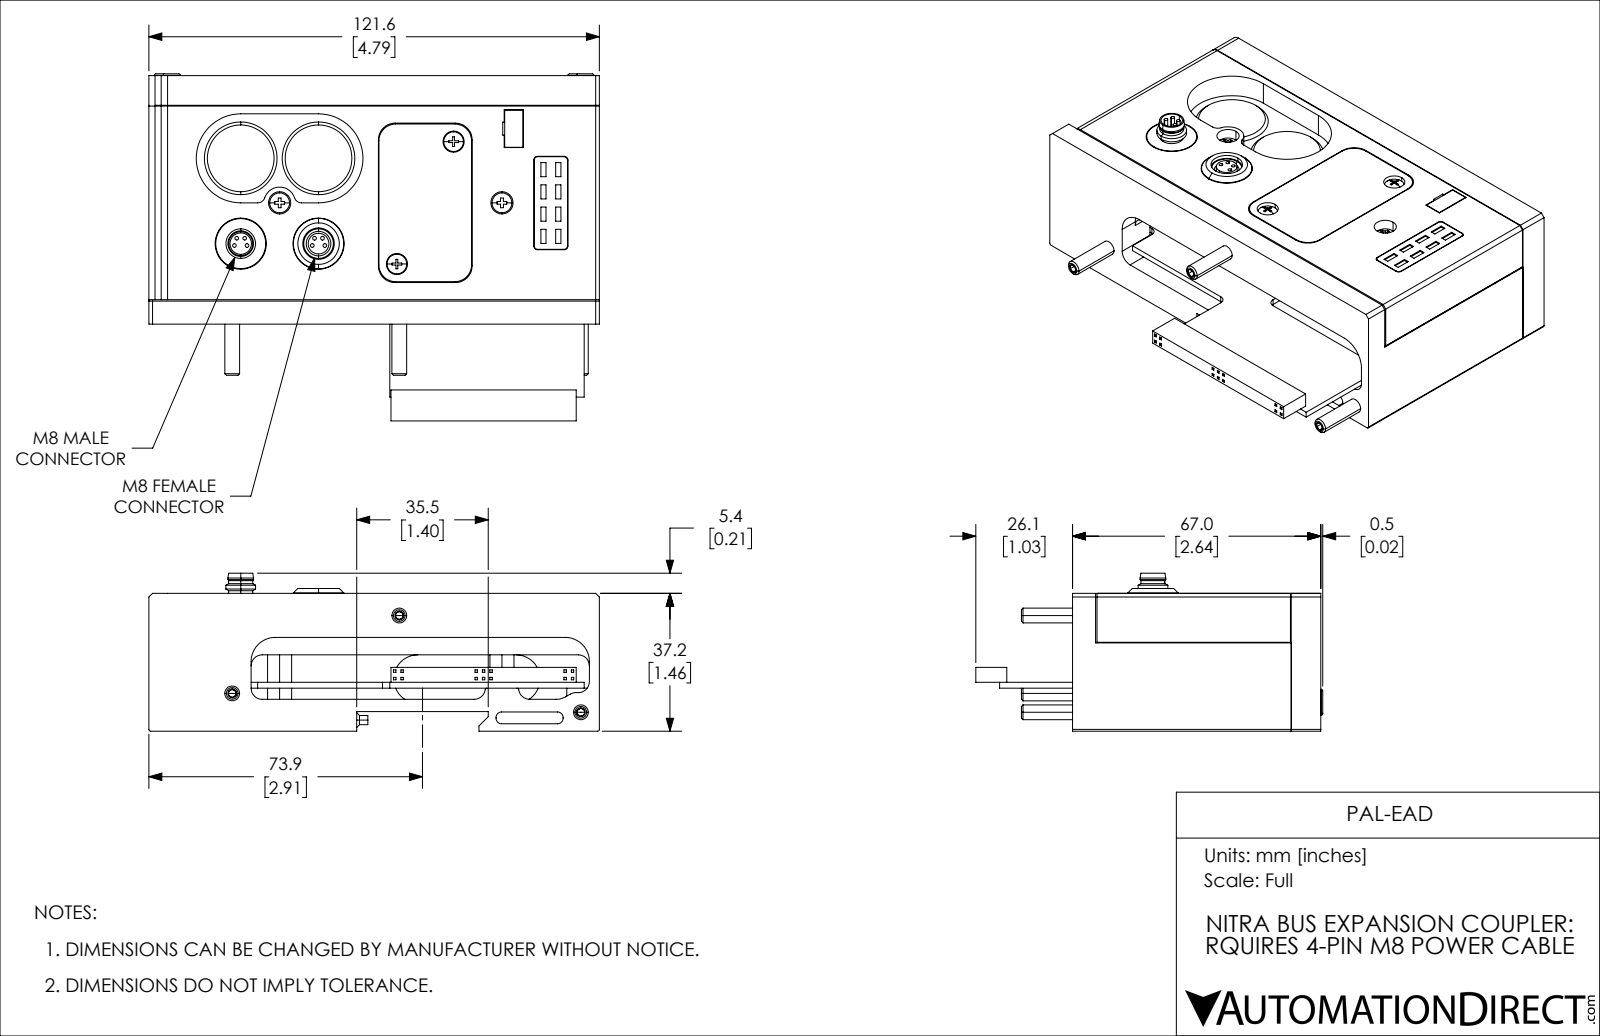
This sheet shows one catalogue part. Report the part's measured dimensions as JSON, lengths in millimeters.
{"part_name": "PAL-EAD", "step_written_by": "SolidWorks 2019 (CONFIG_CONTROL_DESIGN)", "units": "millimeters", "bodies": {"solids": 5, "faces": 860, "planar": 541, "cylindrical": 163, "other": 156}, "overall_size": [121.6, 93.6, 42.6], "volume_mm3": 197800, "surface_area_mm2": 79810, "round_holes": [[3.3, 7], [1, 4], [4.2, 4], [5.7, 2], [6, 2], [7.2, 2], [13.8, 2], [5.8, 1], [6.7, 1], [8.5, 1]], "round_bosses_or_shafts": [[4, 5], [1, 4], [6.5, 3], [7, 2], [5.4, 2], [5.3, 2], [2.5, 2], [13.6, 1]], "partial_cylinders_radius": [[1, 8], [2, 8], [4.5, 8], [3, 7], [0.5, 4], [1.5, 4], [6.5, 4], [12, 2]], "face_to_face_distances": [4, 12.2, 1.6, 24, 13.2, 5.6, 10.6, 11.6, 25.6, 37.2], "hole_center_spacings": [3.4, 1.8, 1.8, 2.1, 15.2, 2.2, 2.7, 7.5]}
